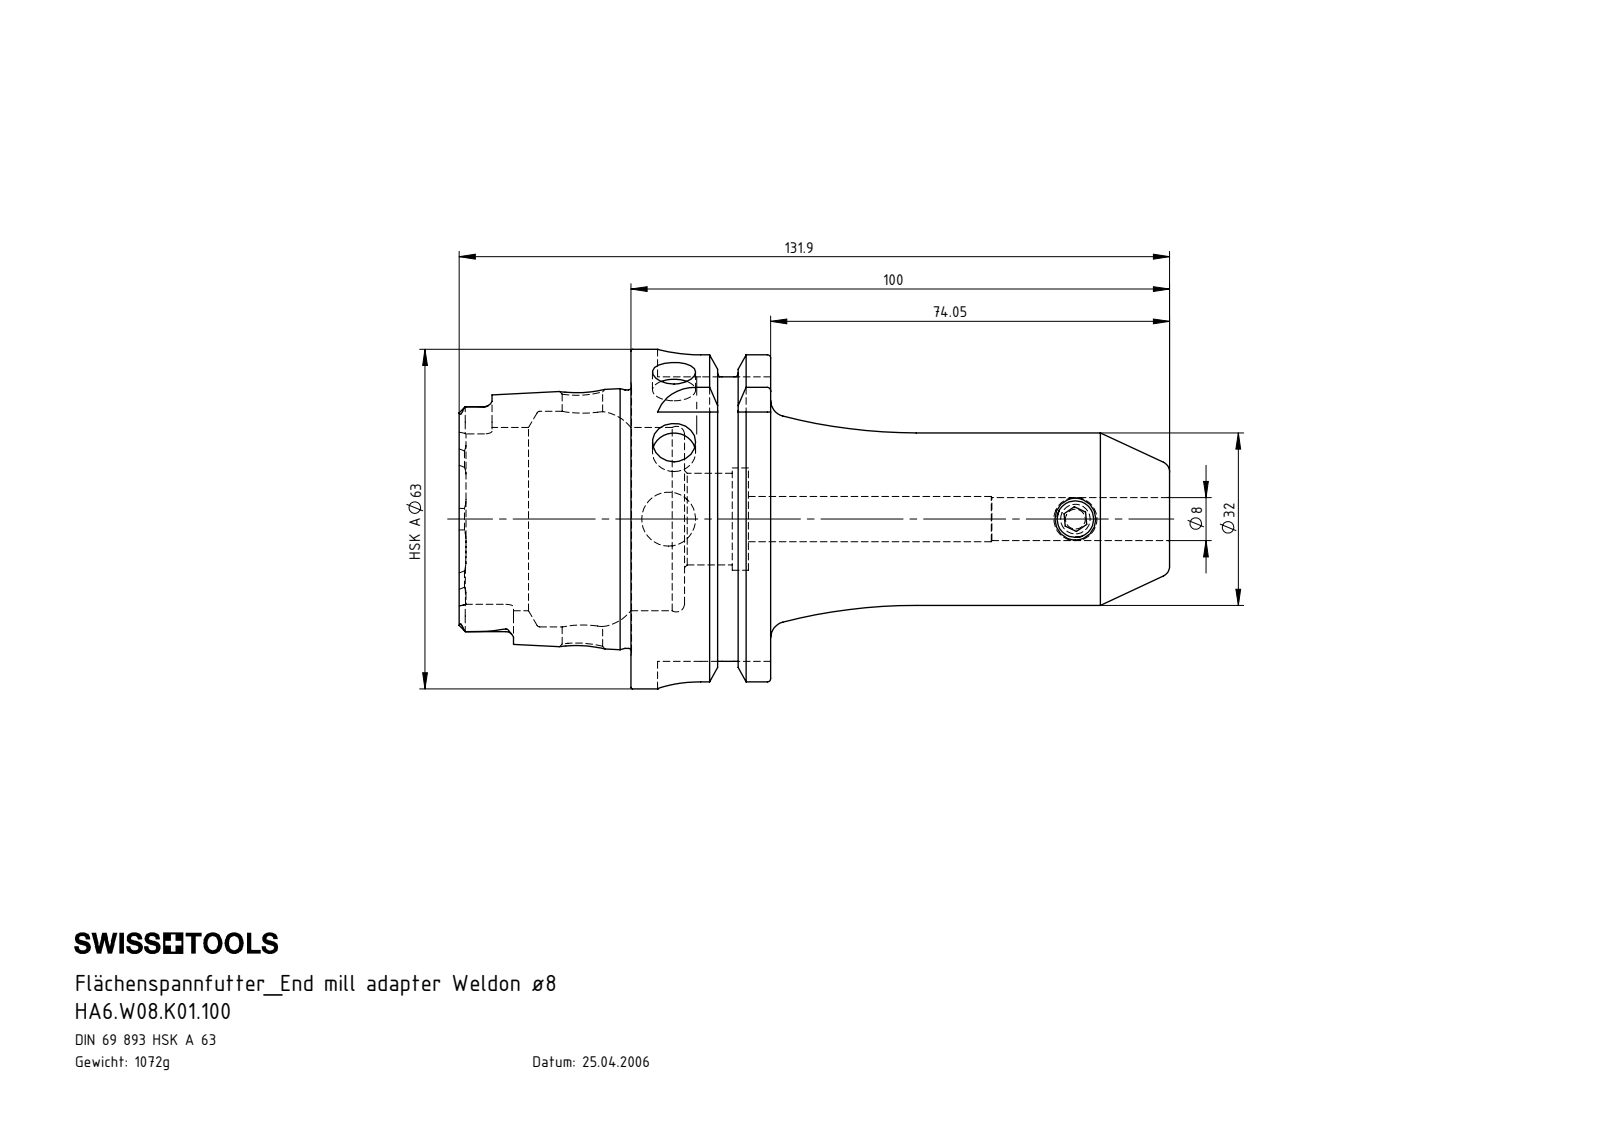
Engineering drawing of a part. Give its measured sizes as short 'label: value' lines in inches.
name: HA6-W08.K01.100; W08-ER1.001.010; HA6-W08.K01.100_B_Fertigbearbeitung
written by: SolidWorks 2012 (AUTOMOTIVE_DESIGN)
unit: in
bodies: 2 solids, 203 faces (57 planar, 55 cylindrical, 91 other)
size: 5.193 × 2.48 × 2.48
volume: 8.334 in³; area: 48.83 in²
holes: 3× ⌀0.315, 1× ⌀0.268, 1× ⌀0.295, 1× ⌀0.331, 1× ⌀0.394, 1× ⌀0.669, 1× ⌀0.748, 1× ⌀1.339, 1× ⌀1.575
bosses: 1× ⌀2.48, 1× ⌀2.163, 1× ⌀1.887, 1× ⌀1.26, 1× ⌀0.315
rounds: 6× R0.055, 4× R0.113, 4× R0.315
face distances: 1.022, 0.63, 0.392, 1.256, 1.648, 2.278, 2.079, 0.858, 0.467, 2.114
hole spacings: 2.972
